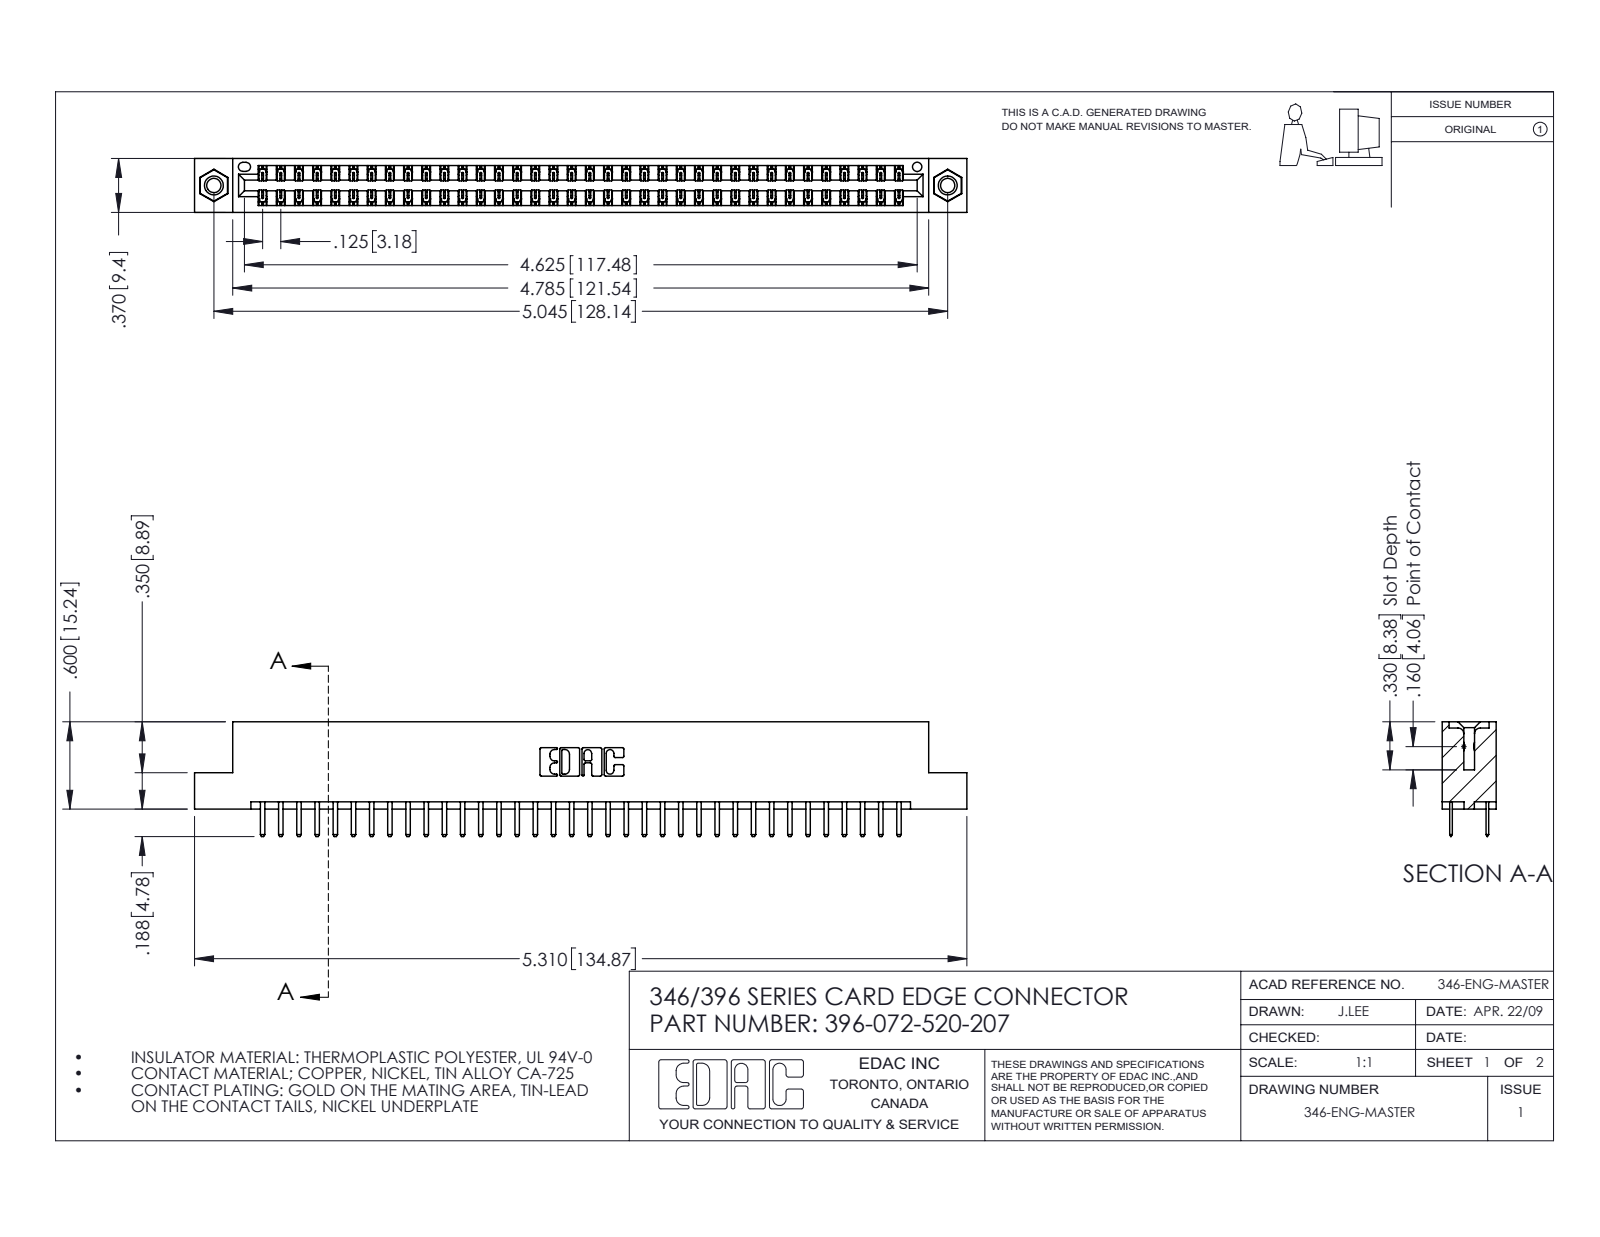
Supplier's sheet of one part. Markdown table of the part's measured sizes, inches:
| quantity | value |
| --- | --- |
| part name | 345-292-001_345-293-120; 345-250-001_345-250-005-103; 346 Part_Flush Mounting Lugs - 0.156 Dia-TI; 396-072-520-207 |
| STEP written by | SolidWorks 2016 (CONFIG_CONTROL_DESIGN) |
| units | inches |
| bodies | 75 solids, 4214 faces (2772 planar, 1426 cylindrical, 16 other) |
| overall size | 5.31 × 0.788 × 0.37 |
| volume | 0.797 in³ |
| surface area | 27.62 in² |
| round holes (diameter × count) | 0.098 × 2, 0.125 × 2, 0.156 × 2, 0.064 × 1 |
| round bosses / shafts (diameter × count) | 0.155 × 2 |
| partial cylindrical surfaces (radius × count) | 0.006 × 108, 0.01 × 76, 0.01 × 22, 0.007 × 6, 0.031 × 6, 0.026 × 3, 0.014 × 2, 0.022 × 2 |
| main face-to-face distances | 0.048, 0.322, 0.25, 0.37, 0.275, 0.072, 0.298, 0.025, 0.148, 0.222 |
| hole center spacings | 0.246, 4.836, 5.045 |
